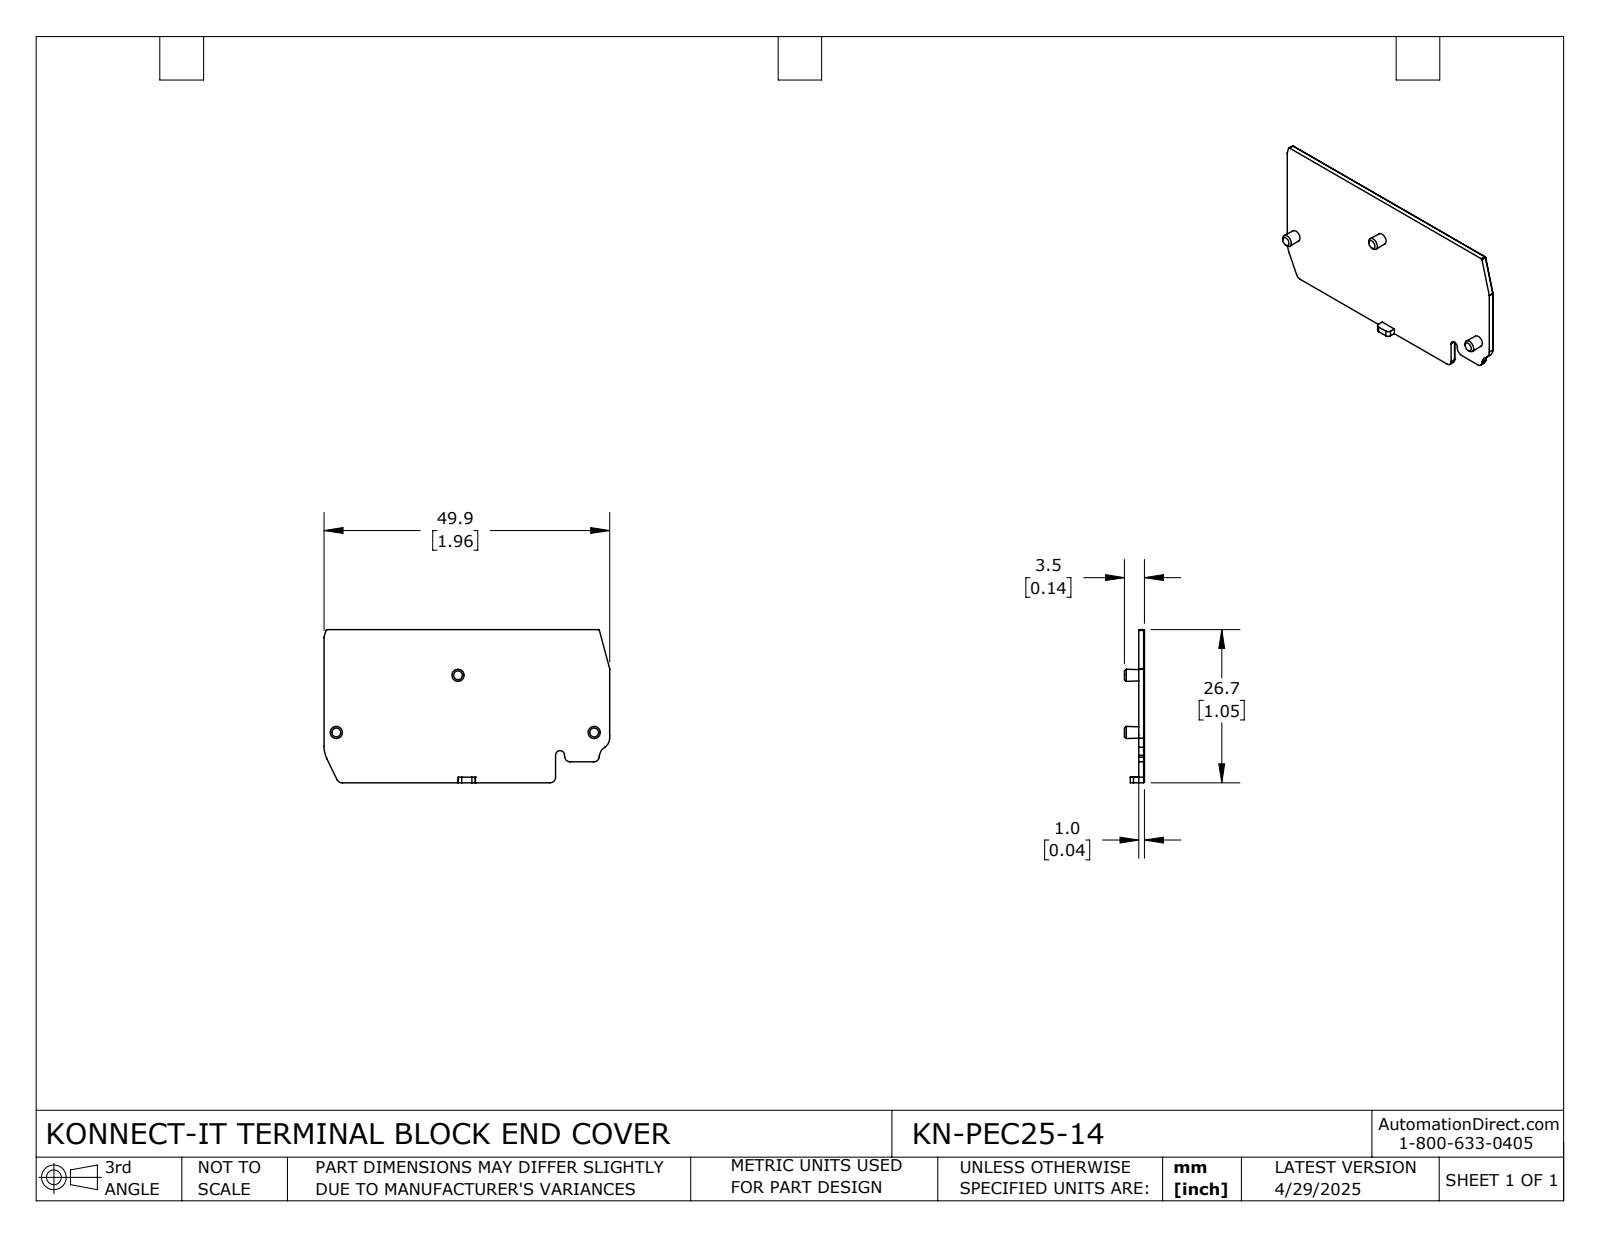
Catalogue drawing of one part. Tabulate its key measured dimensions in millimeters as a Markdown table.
| quantity | value |
| --- | --- |
| part name | KN-PEC25-14 |
| STEP written by | SolidWorks 2024 (CONFIG_CONTROL_DESIGN) |
| units | millimeters |
| bodies | 1 solid, 71 faces (32 planar, 27 cylindrical, 12 other) |
| overall size | 49.9 × 26.7 × 3.5 |
| volume | 1 300 mm³ |
| surface area | 2 763 mm² |
| partial cylindrical surfaces (radius × count) | 0.2 × 4, 0.9 × 4, 1 × 4, 0.3 × 3, 0.6 × 2, 0.1 × 1, 0.8 × 1, 0.9 × 1 |
| main face-to-face distances | 1, 26.7, 0.8, 26.6, 49.9, 2.5, 3.4, 3.5, 26.5, 49.8 |
